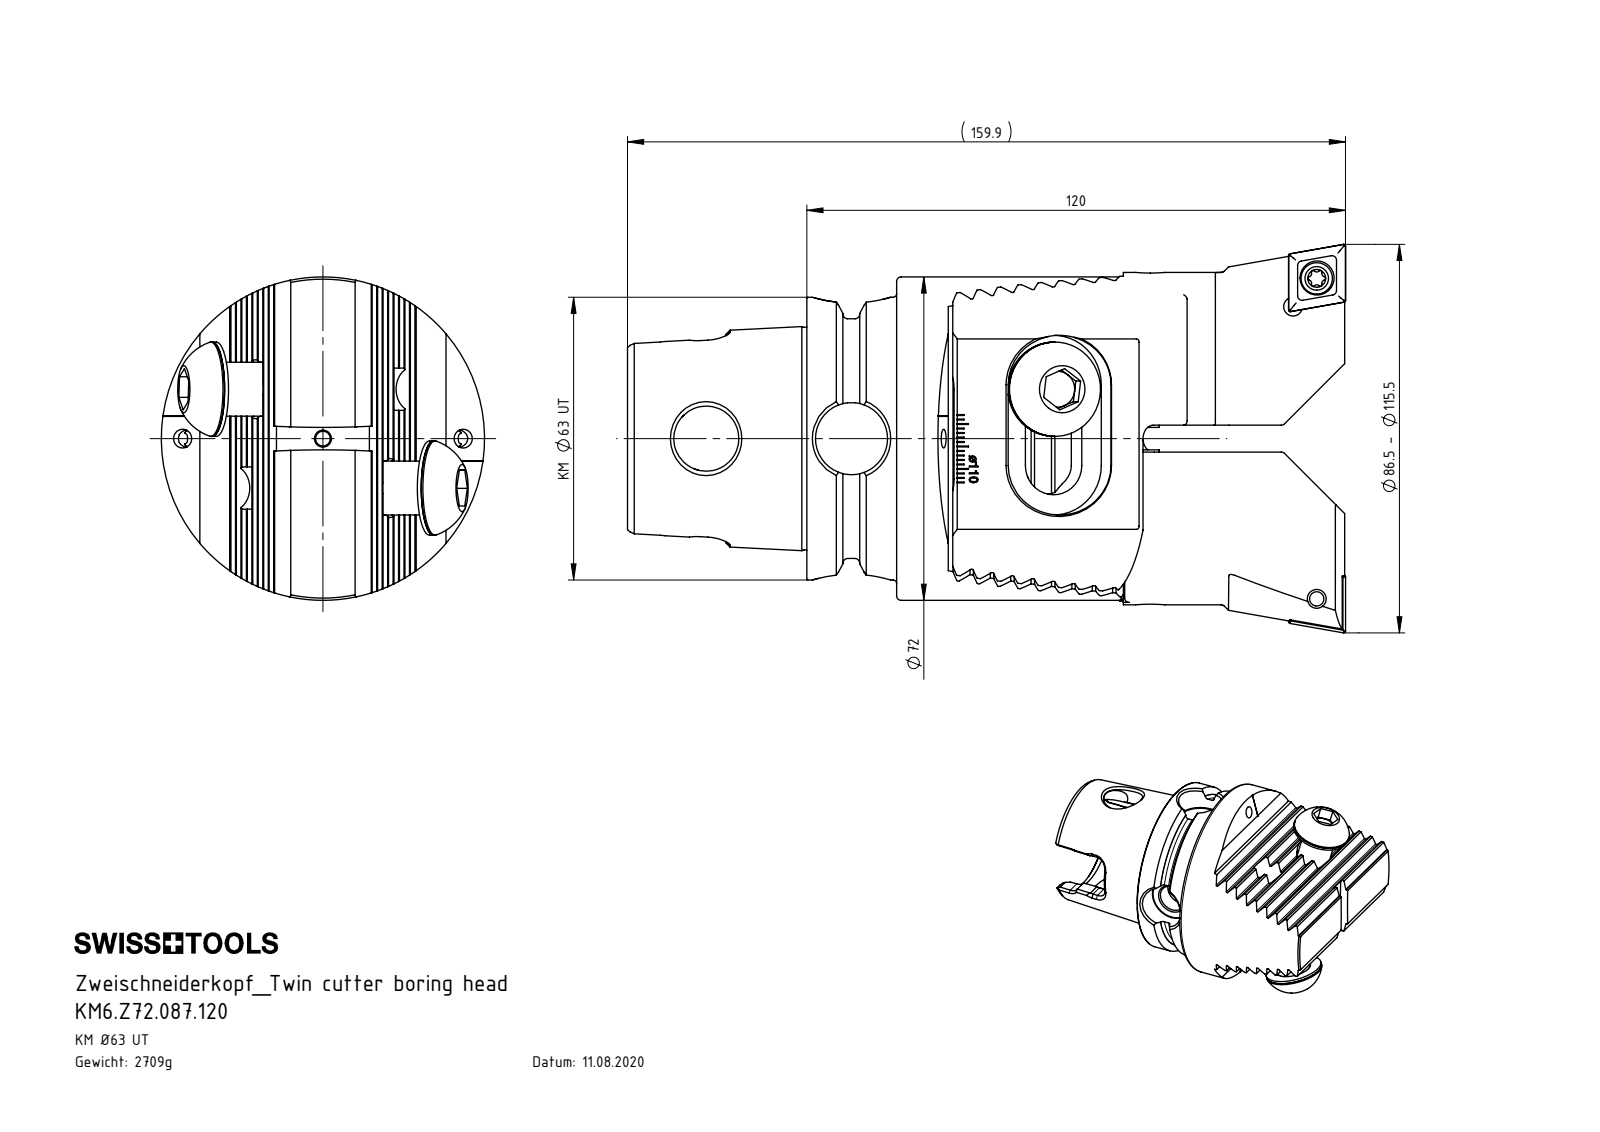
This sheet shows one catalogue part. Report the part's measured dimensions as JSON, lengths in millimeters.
{"part_name": "KU6-Z72.K23.120_D; KU6.Z72.K23.120; Z72-ER1.002.025_A; Z72-ER1.001.025 (+1 more)", "step_written_by": "SolidWorks 2017 (AUTOMOTIVE_DESIGN)", "units": "millimeters", "bodies": {"solids": 5, "faces": 386, "planar": 184, "cylindrical": 88, "other": 114}, "overall_size": [110.45, 72, 72], "volume_mm3": 202156, "surface_area_mm2": 43262, "round_holes": [[4.2, 3], [10.25, 2], [13, 2], [13.5, 2], [16.05, 2], [3.3, 1], [8.5, 1], [10.1, 1], [12.1, 1], [14.5, 1], [31.1, 1], [35.27, 1]], "round_bosses_or_shafts": [[21, 2], [12, 2], [72, 1], [62.95, 1]], "partial_cylinders_radius": [[0.34, 18], [4, 6], [7.04, 2], [220, 2], [27.85, 1]], "face_to_face_distances": [4.07, 8.14, 12.21, 20.36, 16.28, 16.29, 24.43, 12.22, 28.5, 20.35], "hole_center_spacings": [14.05, 32.35, 46.4]}
